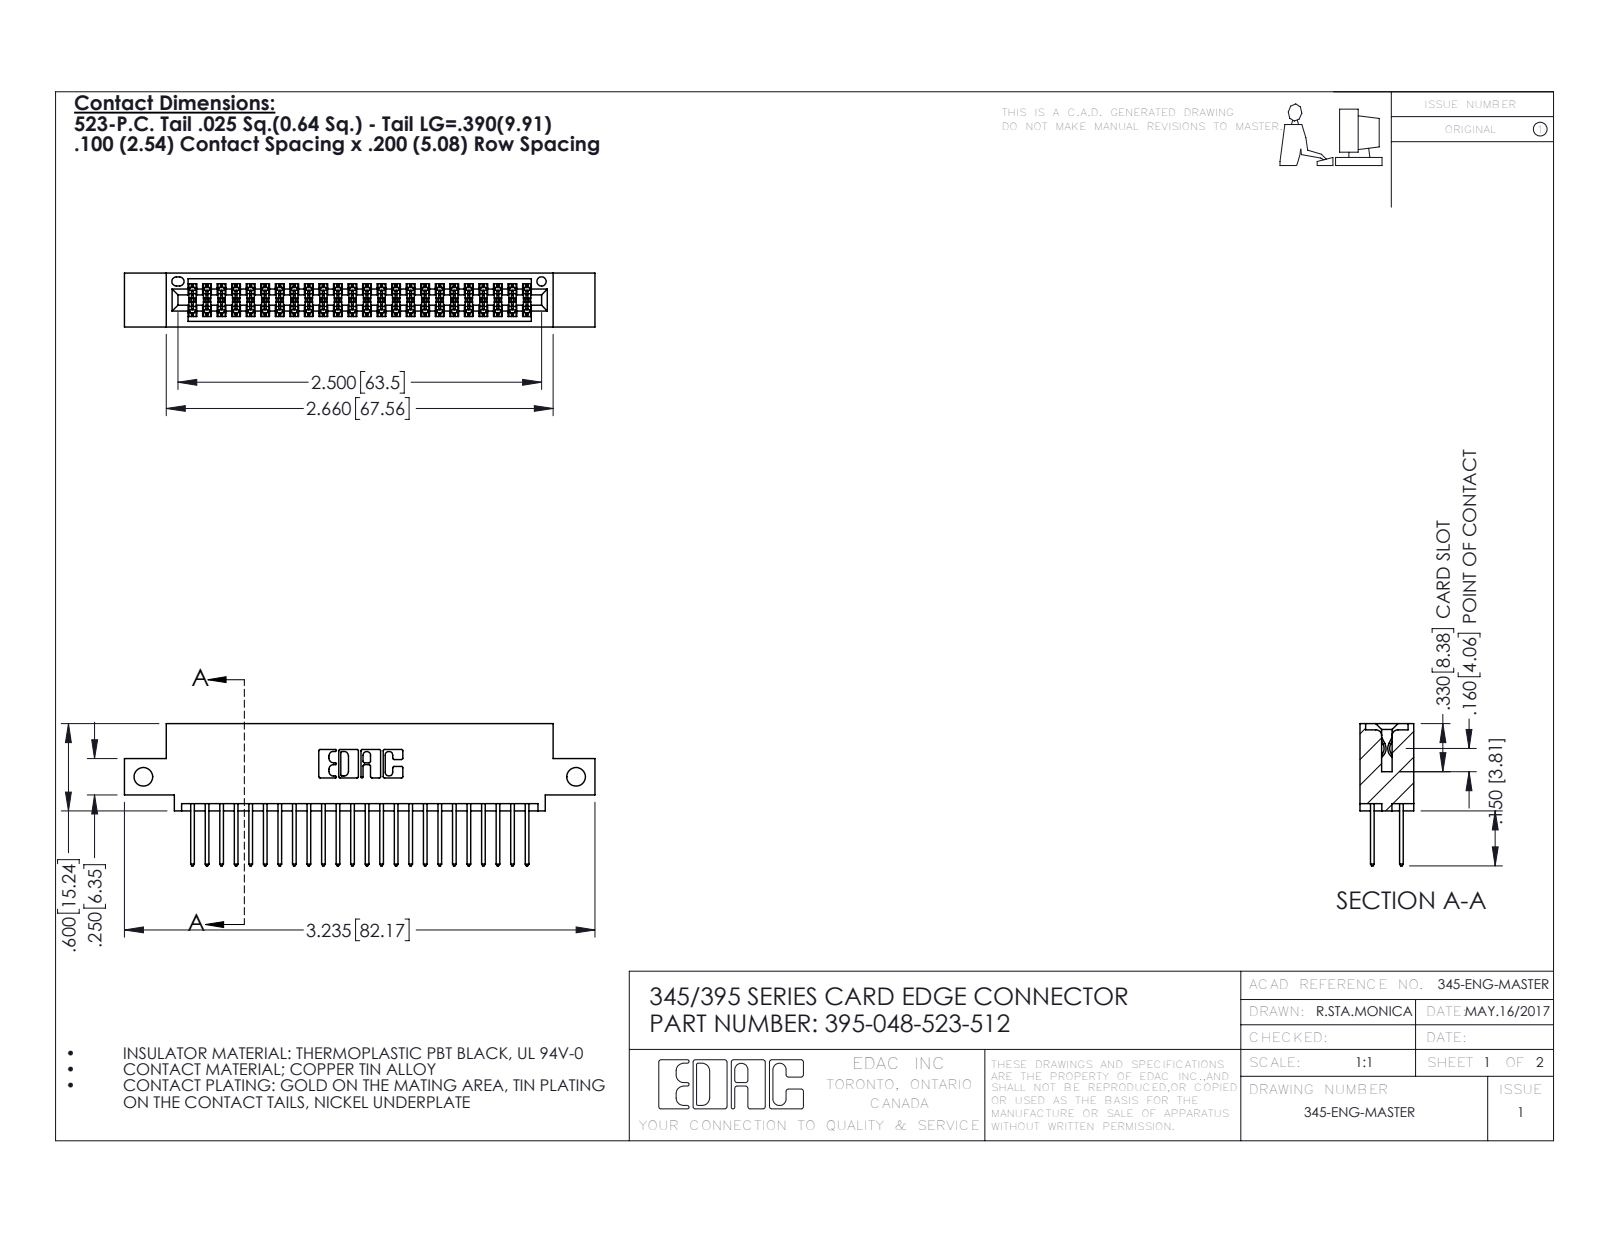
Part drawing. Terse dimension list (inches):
name: 345 Part_0.110 Offset - Side Mount; 395-048-523-512; 345-292-001_345-293-123
written by: SolidWorks 2016 (CONFIG_CONTROL_DESIGN)
unit: in
bodies: 49 solids, 2530 faces (1668 planar, 862 cylindrical, 0 other)
size: 3.235 × 0.977 × 0.37
volume: 0.473 in³; area: 17.84 in²
holes: 2× ⌀0.128, 1× ⌀0.064
rounds: 72× R0.006, 48× R0.01, 22× R0.01, 6× R0.007, 6× R0.031, 3× R0.026, 2× R0.014, 2× R0.019
face distances: 0.298, 0.072, 0.2, 0.098, 0.272, 0.025, 0.37, 0.225, 0.175, 0.149
hole spacings: 2.975
